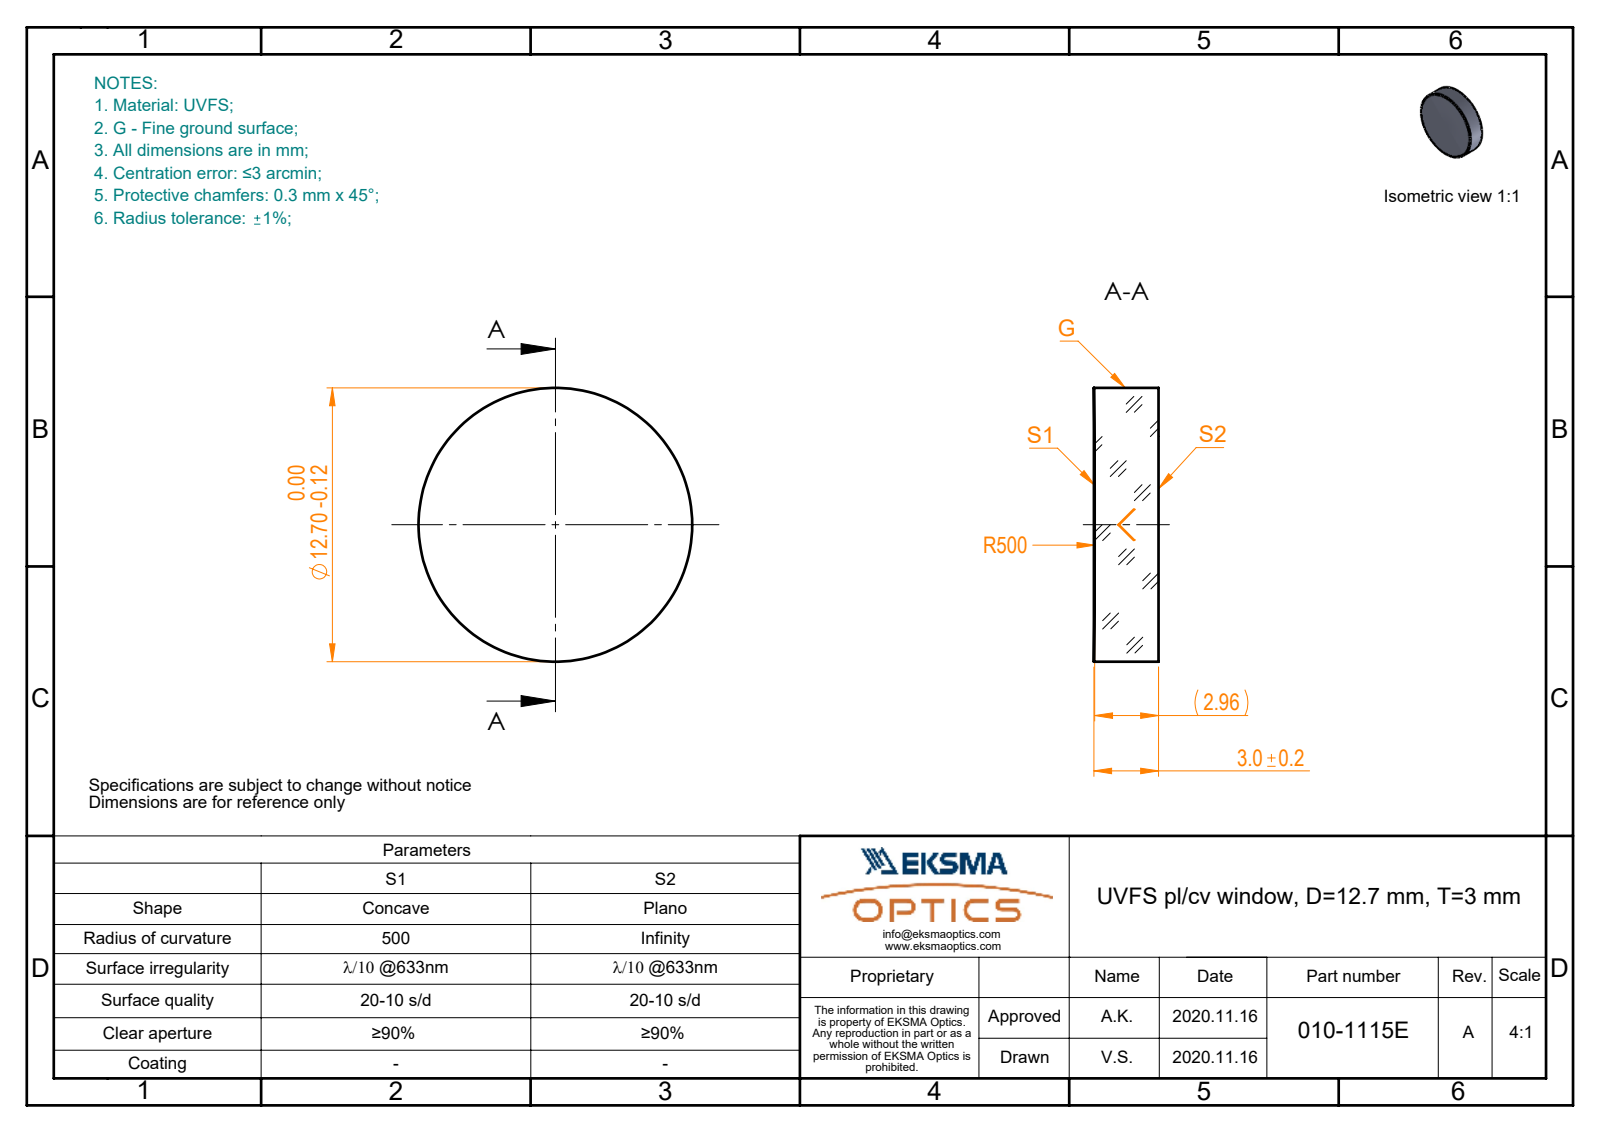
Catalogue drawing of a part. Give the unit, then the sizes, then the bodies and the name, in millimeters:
Units: millimetres
Overall size (bounding box): 12.7 × 12.7 × 3
Round bosses / shafts (diameter × count): ⌀12.7 ×1
Volume: 377 mm³ · Surface area: 373 mm²
Bodies: 1 solid, 5 faces (1 planar, 2 cylindrical, 2 other)
Part name (STEP PRODUCT): 010-1115E_UVFS_PCV_window
STEP written by: SolidWorks 2019 (CONFIG_CONTROL_DESIGN)
